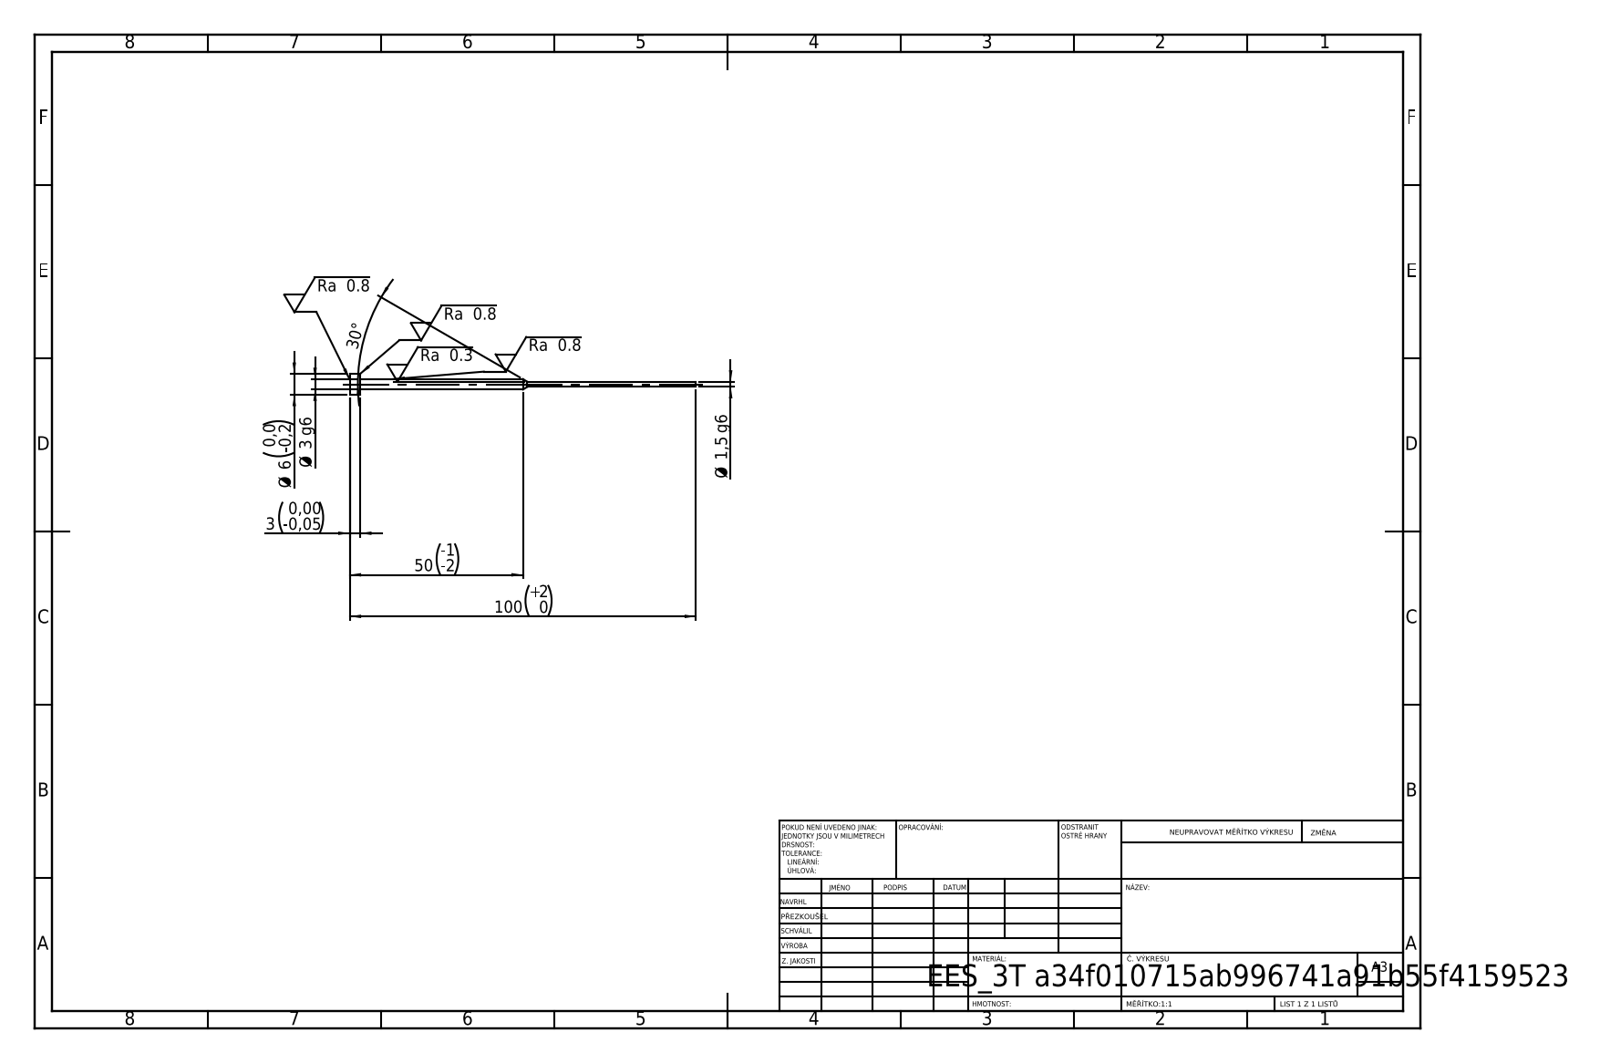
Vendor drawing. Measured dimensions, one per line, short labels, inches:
written by: SolidWorks 2019 (CONFIG_CONTROL_DESIGN)
unit: in
bodies: 1 solid, 11 faces (3 planar, 6 cylindrical, 2 other)
size: 3.937 × 0.236 × 0.236
volume: 0.031 in³; area: 1.23 in²
bosses: 1× ⌀0.236, 1× ⌀0.118, 1× ⌀0.059
face distances: 0.118, 3.819, 3.937
